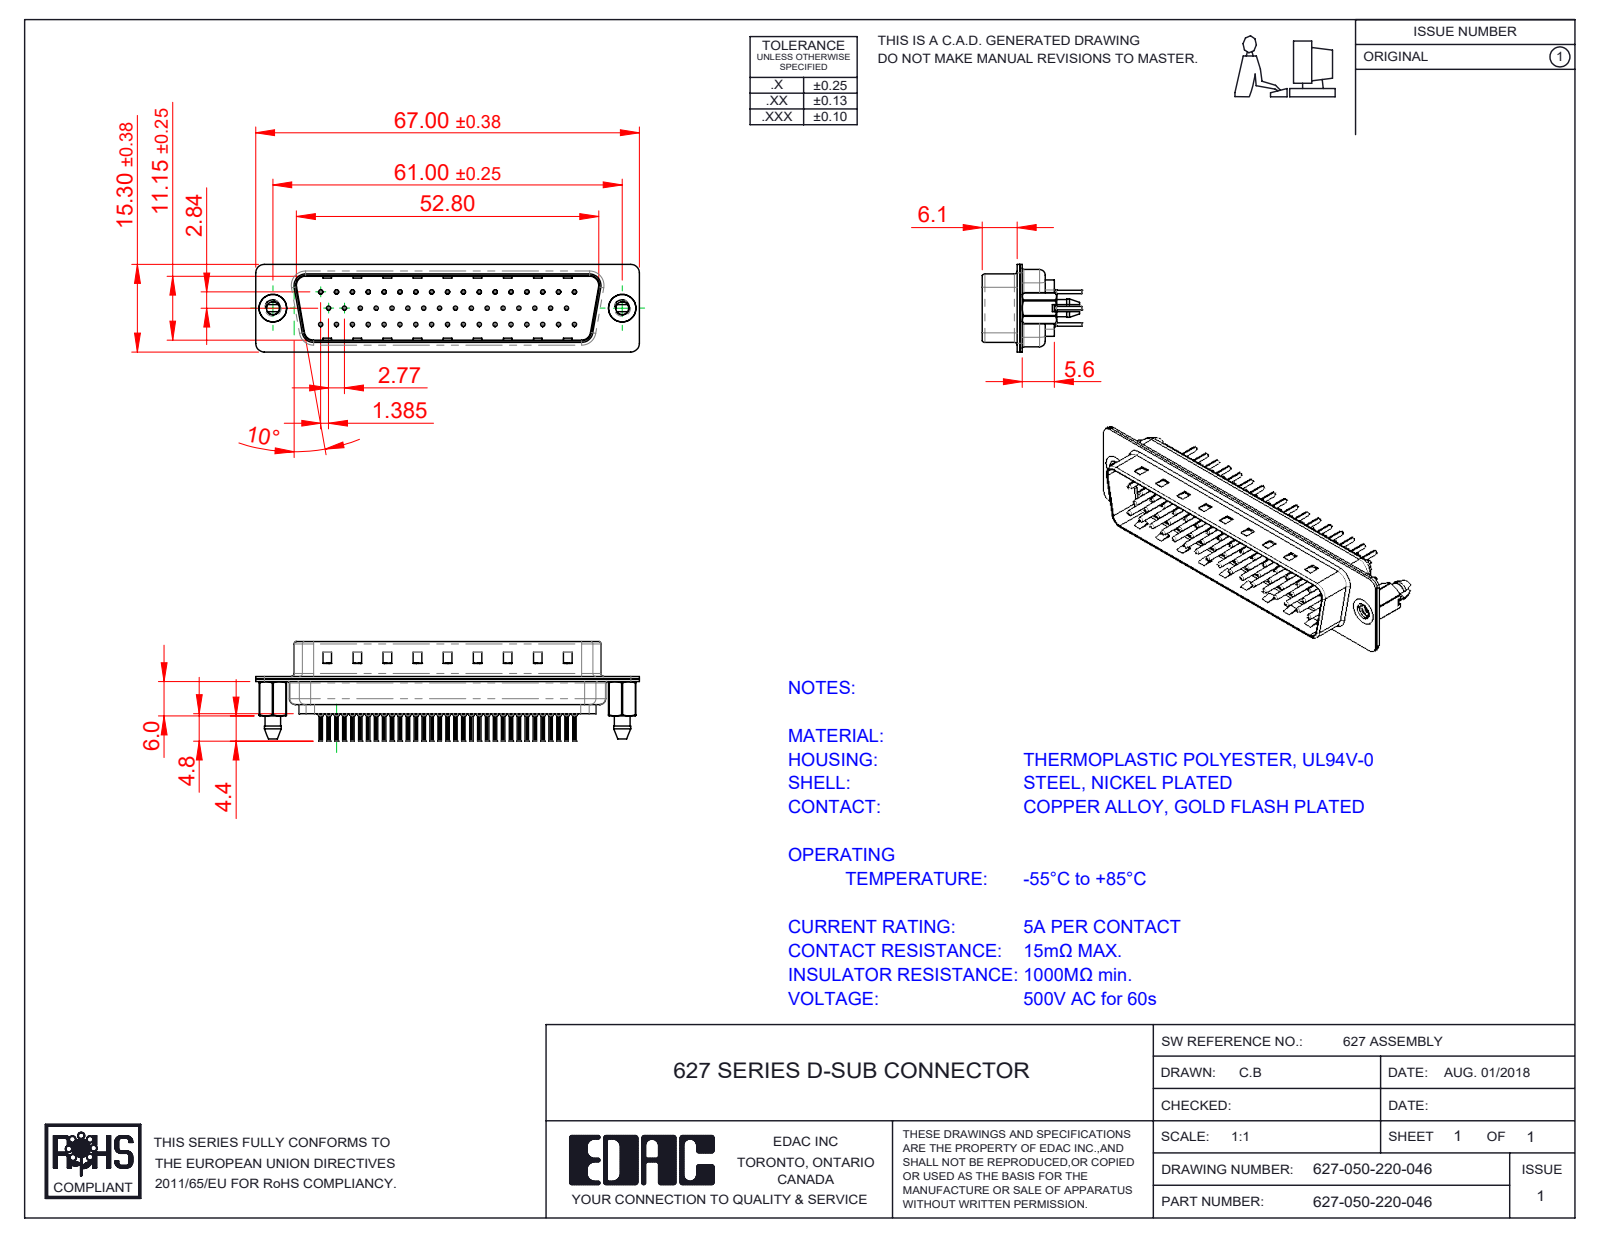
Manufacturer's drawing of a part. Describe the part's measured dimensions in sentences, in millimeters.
The part is named "627 Housing_50 LP; 627 Contact Row 2_20L; 627 Contact Row 3_20L; 627 Contact Row 1_20L (+4 more)". Its 3-D file was written by "SolidWorks 2020 (CONFIG_CONTROL_DESIGN)". It is 55 solids with 5386 faces: 1435 planar, 2023 cylindrical and 1928 other. Overall it measures 67 by 17.3 by 15.3 millimeters. Its volume is 4 539 cubic millimeters and its surface area 12 876 square millimeters. Round holes: 50 of diameter 0.2, 50 of diameter 0.35, 50 of diameter 1.1, 50 of diameter 1.6, 2 of diameter 2.26, 2 of diameter 4, 2 of diameter 4.8. Round bosses or shafts: 50 of diameter 2, 50 of diameter 1.5, 50 of diameter 0.75, 50 of diameter 0.6, 2 of diameter 4.9. Partial cylindrical surfaces (rounded edges, fillets, slot ends): 100 of radius 0.1, 18 of radius 1.5, 12 of radius 2, 10 of radius 1.6, 8 of radius 0.5, 4 of radius 0.25, 4 of radius 0.6, 4 of radius 0.65. The main face-to-face distances are 0.4, 0.45, 11.55, 6.05, 0.9, 6.5, 0.78, 12.33, 1.95, 0.77. The hole center spacings are 3.16, 2.77, 5.54, 8.31, 11.08, 13.85, 16.62, 5.03.
